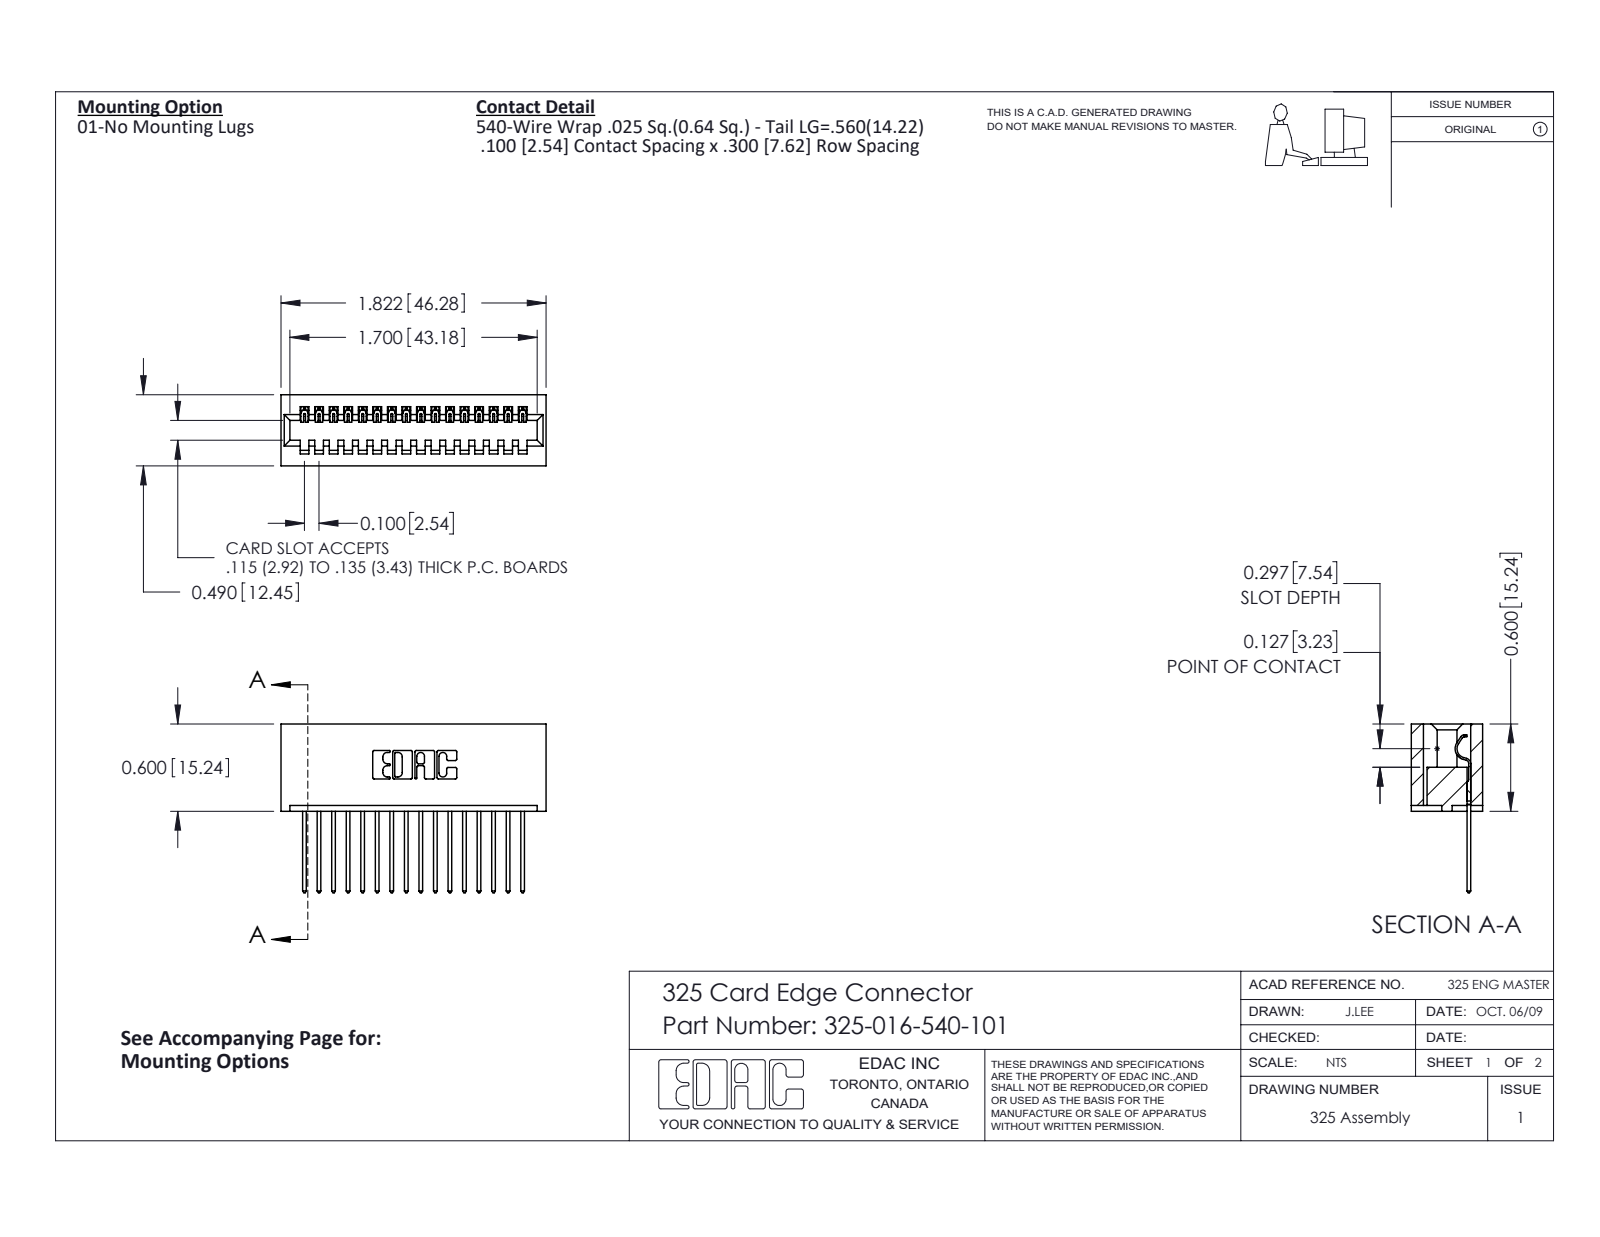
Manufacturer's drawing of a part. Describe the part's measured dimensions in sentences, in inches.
The part is named "325-016-540-101; 325 Part_Lugless; 325-292-001_325-293-140". Its 3-D file was written by "SolidWorks 2016 (CONFIG_CONTROL_DESIGN)". It is 17 solids with 1034 faces: 738 planar, 296 cylindrical and 0 other. Overall it measures 1.822 by 1.16 by 0.49 inches. Its volume is 0.382 cubic inches and its surface area 10.93 square inches. Partial cylindrical surfaces (rounded edges, fillets, slot ends): 32 of radius 0.006, 32 of radius 0.01, 22 of radius 0.01, 6 of radius 0.007, 6 of radius 0.031, 3 of radius 0.026, 1 of radius 0.014, 1 of radius 0.022. The main face-to-face distances are 0.083, 0.407, 0.3, 0.49, 0.107, 0.383, 0.025, 0.1, 0.2, 0.4.
